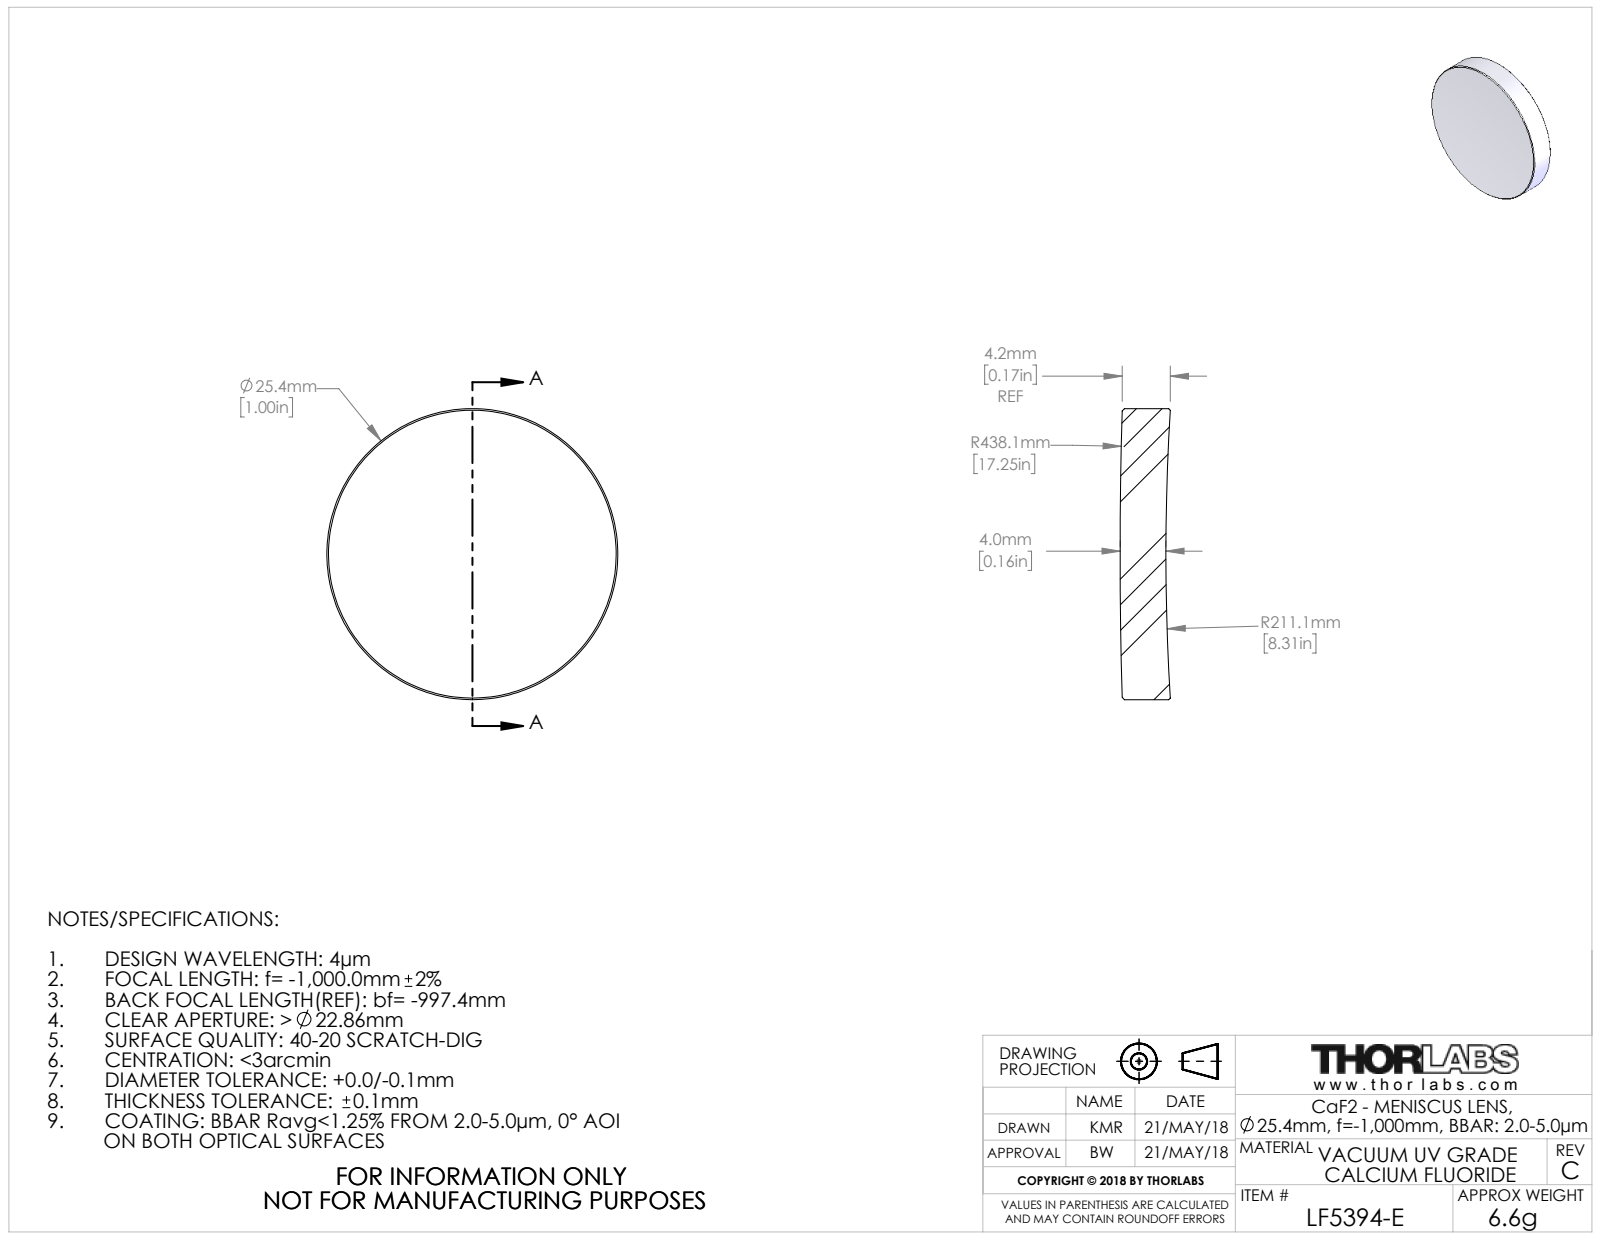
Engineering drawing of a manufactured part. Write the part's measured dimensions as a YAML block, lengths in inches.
part_name: "20180-E0W"
step_written_by: "SolidWorks 2016 (CONFIG_CONTROL_DESIGN)"
units: inches
bodies: {solids: 1, faces: 10, planar: 0, cylindrical: 2, other: 8}
overall_size: [1, 1, 0.172]
volume: 0.127
surface_area: 2.065
round_bosses_or_shafts:
  - {diameter: 1, count: 1}
